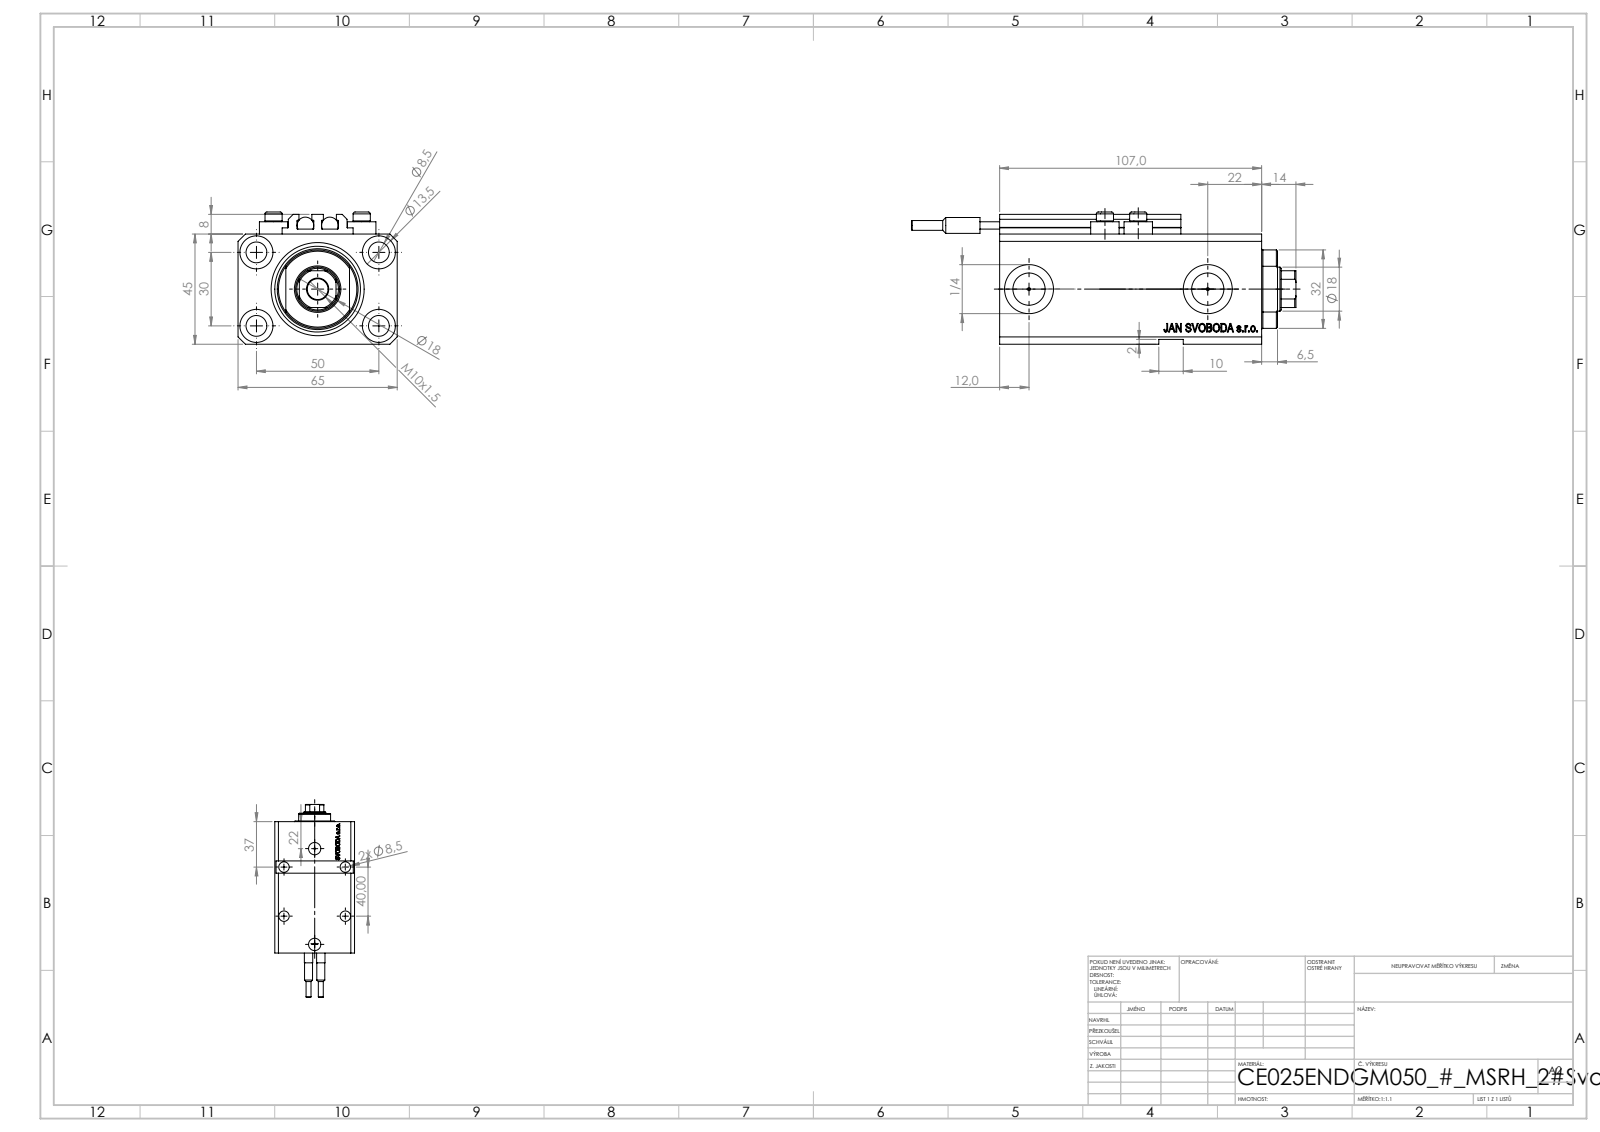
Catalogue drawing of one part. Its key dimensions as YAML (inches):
part_name: "V250CE_VC_E; SWITCH_V250CE; ALLEN BOLT V250CE; V250CE_C_VCP (+1 more)"
step_written_by: "SolidWorks 2019 (CONFIG_CONTROL_DESIGN)"
units: inches
bodies: {solids: 10, faces: 1155, planar: 547, cylindrical: 170, other: 438}
overall_size: [6.181, 2.559, 2.126]
volume: 16.68
surface_area: 125.2
round_holes:
  - {diameter: 0.335, count: 9}
  - {diameter: 0.049, count: 4}
  - {diameter: 0.157, count: 4}
  - {diameter: 0.531, count: 4}
  - {diameter: 0.394, count: 2}
  - {diameter: 0.518, count: 2}
  - {diameter: 0.787, count: 2}
  - {diameter: 0.709, count: 1}
  - {diameter: 0.984, count: 1}
  - {diameter: 1.496, count: 1}
round_bosses_or_shafts:
  - {diameter: 0.457, count: 4}
  - {diameter: 0.276, count: 4}
  - {diameter: 0.268, count: 2}
  - {diameter: 0.256, count: 2}
  - {diameter: 0.157, count: 2}
partial_cylinders:
  - {radius: 0.008, count: 10}
  - {radius: 0.335, count: 1}
  - {radius: 0.63, count: 1}
face_to_face_distances: [1.772, 2.559, 0.079, 1.85, 3.661, 0.118, 0.551, 4.213, 0.394, 0.197]
hole_center_spacings: [1.148, 1.969, 0.535, 0.581, 0.595, 1.083, 1.098, 1.181]
